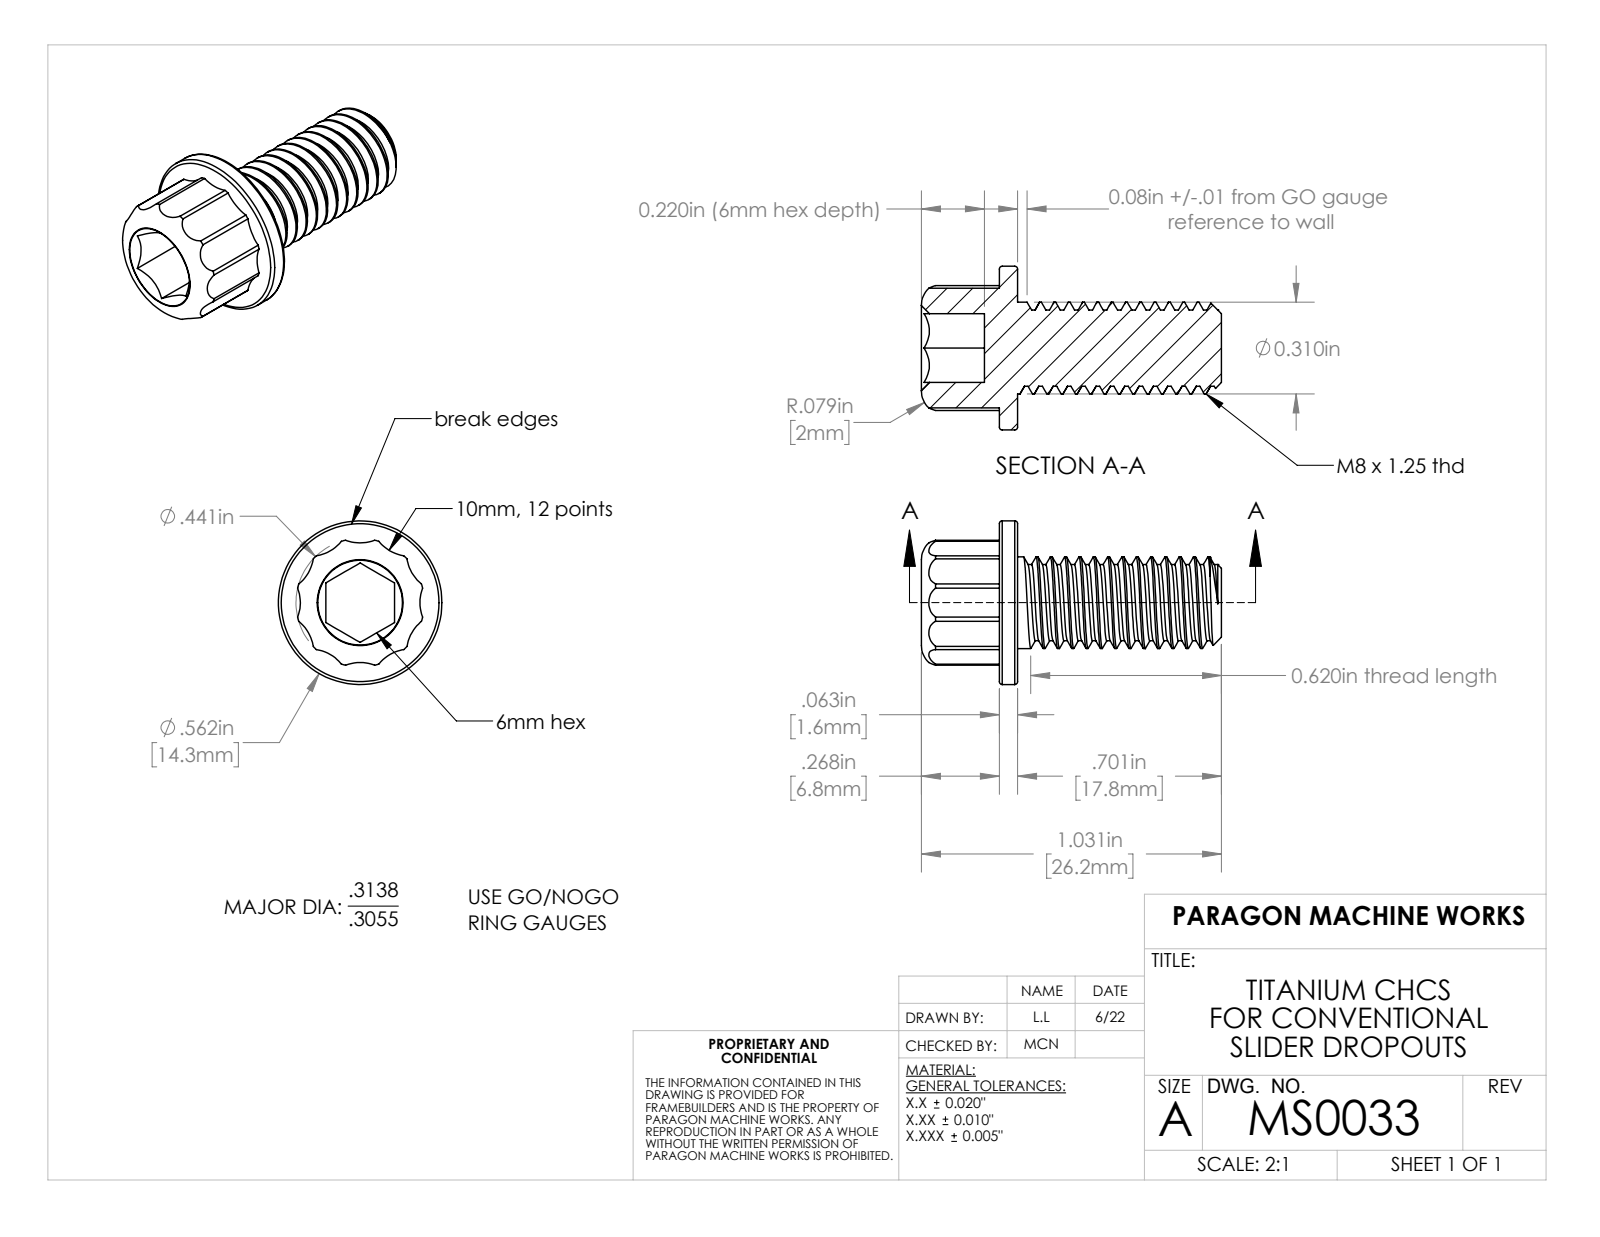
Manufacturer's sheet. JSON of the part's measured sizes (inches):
{"part_name": "MS0033", "step_written_by": "SolidWorks 2023 (AUTOMOTIVE_DESIGN)", "units": "inches", "bodies": {"solids": 1, "faces": 80, "planar": 12, "cylindrical": 54, "other": 14}, "overall_size": [1.031, 0.562, 0.562], "volume_in3": 0.087, "surface_area_in2": 2.072, "round_bosses_or_shafts": [[0.562, 1], [0.315, 1]], "partial_cylinders_radius": [[0.138, 12], [0.22, 1]], "face_to_face_distances": [0.063, 0.236, 0.051, 0.114, 0.815, 0.764, 0.701, 0.217, 0.268, 0.331]}
